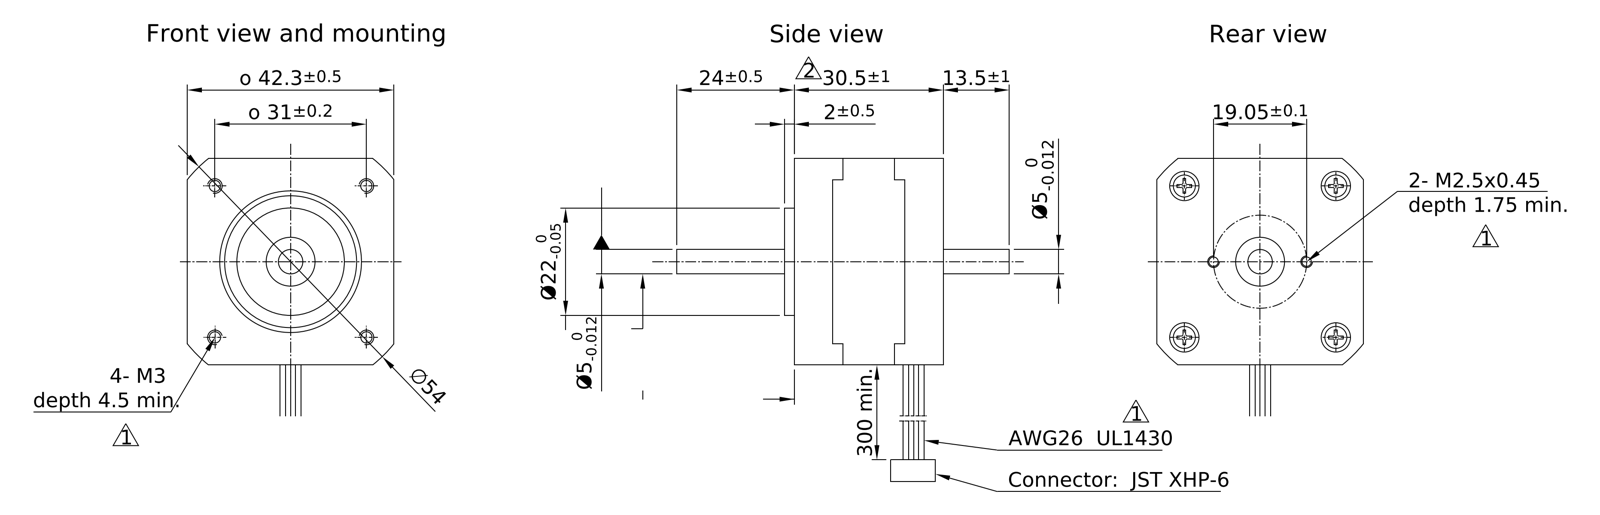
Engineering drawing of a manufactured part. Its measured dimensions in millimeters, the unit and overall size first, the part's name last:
Units: millimetres
Overall size (bounding box): 68 × 54.15 × 42.3
Round holes (diameter × count): ⌀1 ×4, ⌀2.46 ×4, ⌀2.7 ×4, ⌀6 ×4, ⌀2.01 ×2, ⌀5 ×1, ⌀7.5 ×1, ⌀9 ×1
Round bosses / shafts (diameter × count): ⌀2.5 ×4, ⌀2.27 ×4, ⌀22 ×1, ⌀1 ×1
Partial cylindrical surfaces — rounded edges, fillets, slot ends (radius × count): R25 ×1, R27 ×1
Main face-to-face distances: 12.5, 9, 21.5, 42.15, 42, 30.5, 2, 42.3, 11, 19.5
Hole centre spacings: 16.61, 21.92, 29.44, 31, 9.53, 43.84, 1, 2
Volume: 53 440 mm³ · Surface area: 18 013 mm²
Bodies: 10 solids, 263 faces (134 planar, 52 cylindrical, 77 other)
Part name (STEP PRODUCT): ST4118S..._B
STEP written by: Autodesk Inventor 2017 (AUTOMOTIVE_DESIGN)
